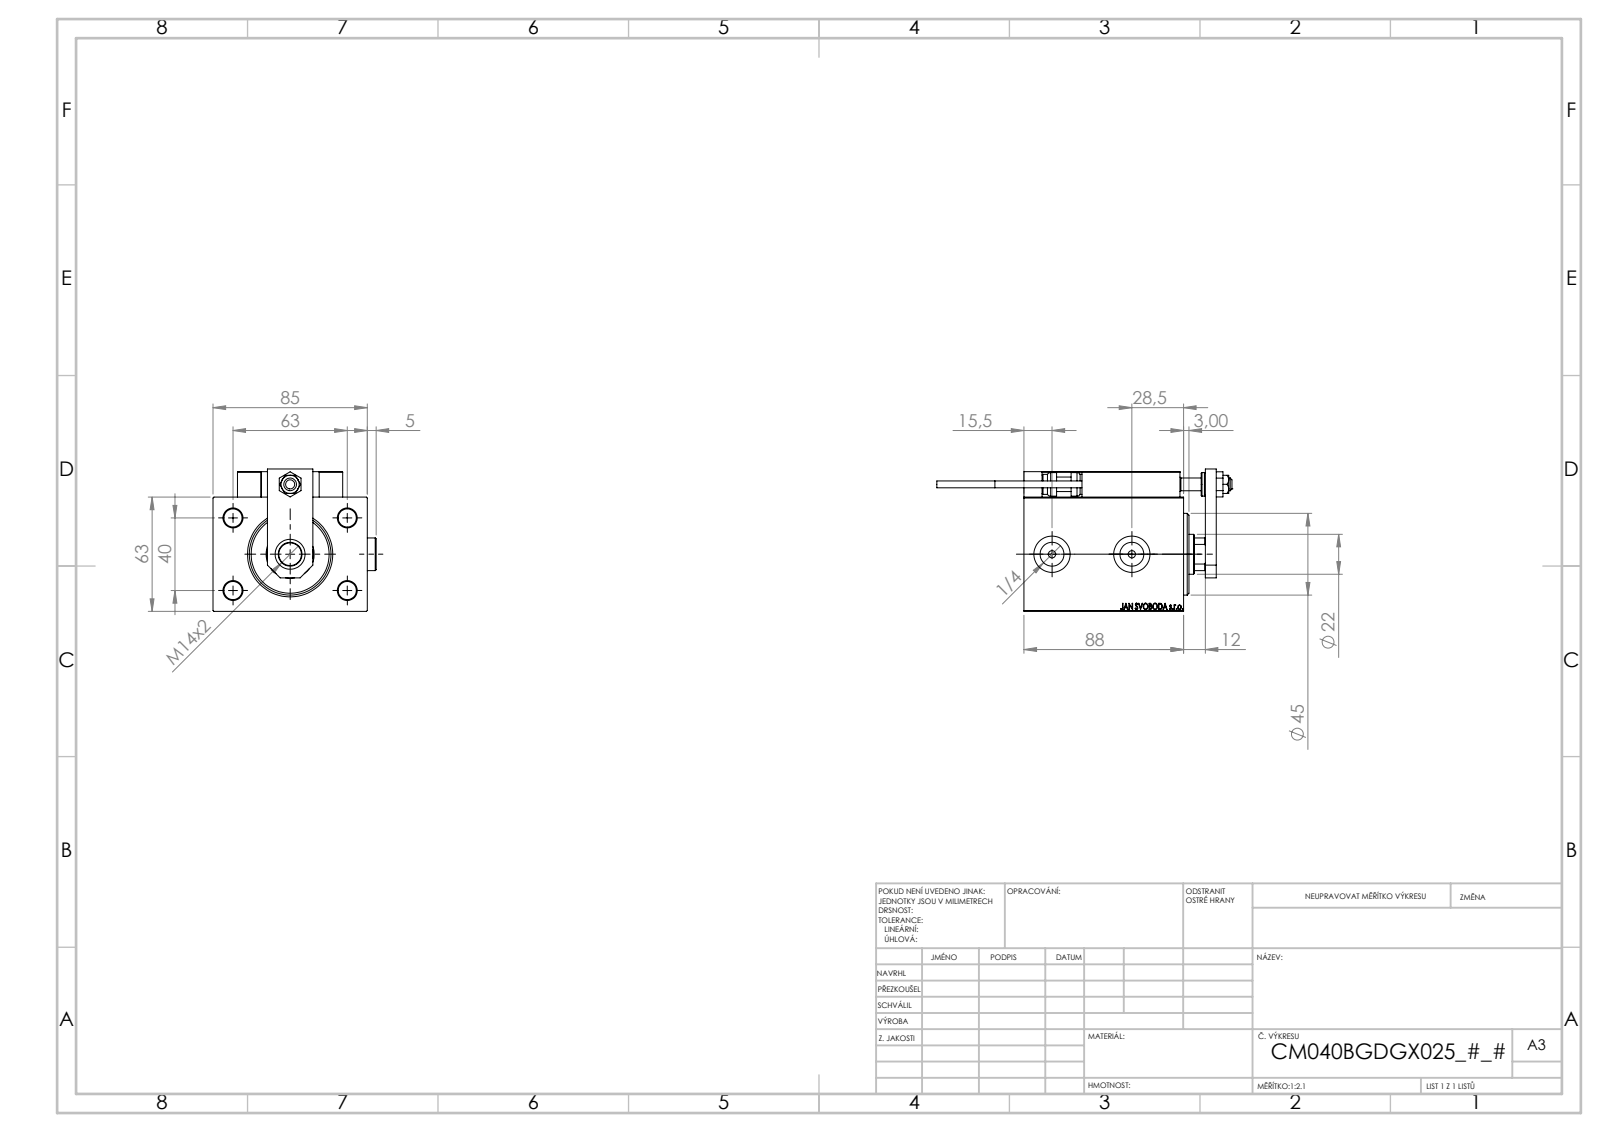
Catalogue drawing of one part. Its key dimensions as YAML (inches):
part_name: "V450CM_B_Body; SWITCH X; ALLEN BOLT D8; V450CM_B_VCP (+8 more)"
step_written_by: "SolidWorks 2019 (CONFIG_CONTROL_DESIGN)"
units: inches
bodies: {solids: 26, faces: 1372, planar: 595, cylindrical: 200, other: 577}
overall_size: [6.406, 3.539, 3.091]
volume: 29.56
surface_area: 151.2
round_holes:
  - {diameter: 0.157, count: 6}
  - {diameter: 0.315, count: 5}
  - {diameter: 0.126, count: 4}
  - {diameter: 0.394, count: 4}
  - {diameter: 0.197, count: 2}
  - {diameter: 0.518, count: 2}
  - {diameter: 0.787, count: 2}
  - {diameter: 0.276, count: 1}
  - {diameter: 0.492, count: 1}
  - {diameter: 0.65, count: 1}
  - {diameter: 0.866, count: 1}
  - {diameter: 1.004, count: 1}
round_bosses_or_shafts:
  - {diameter: 0.709, count: 2}
  - {diameter: 0.197, count: 2}
  - {diameter: 0.15, count: 2}
  - {diameter: 0.512, count: 1}
  - {diameter: 0.433, count: 1}
partial_cylinders:
  - {radius: 0.012, count: 30}
  - {radius: 0.118, count: 2}
  - {radius: 0.413, count: 1}
face_to_face_distances: [2.48, 0.472, 3.346, 3.465, 2.992, 0.551, 0.984, 3.031, 0.709, 1.181]
hole_center_spacings: [1.469, 0.448, 0.787, 1.165, 1.169, 1.42, 1.438, 1.575]
